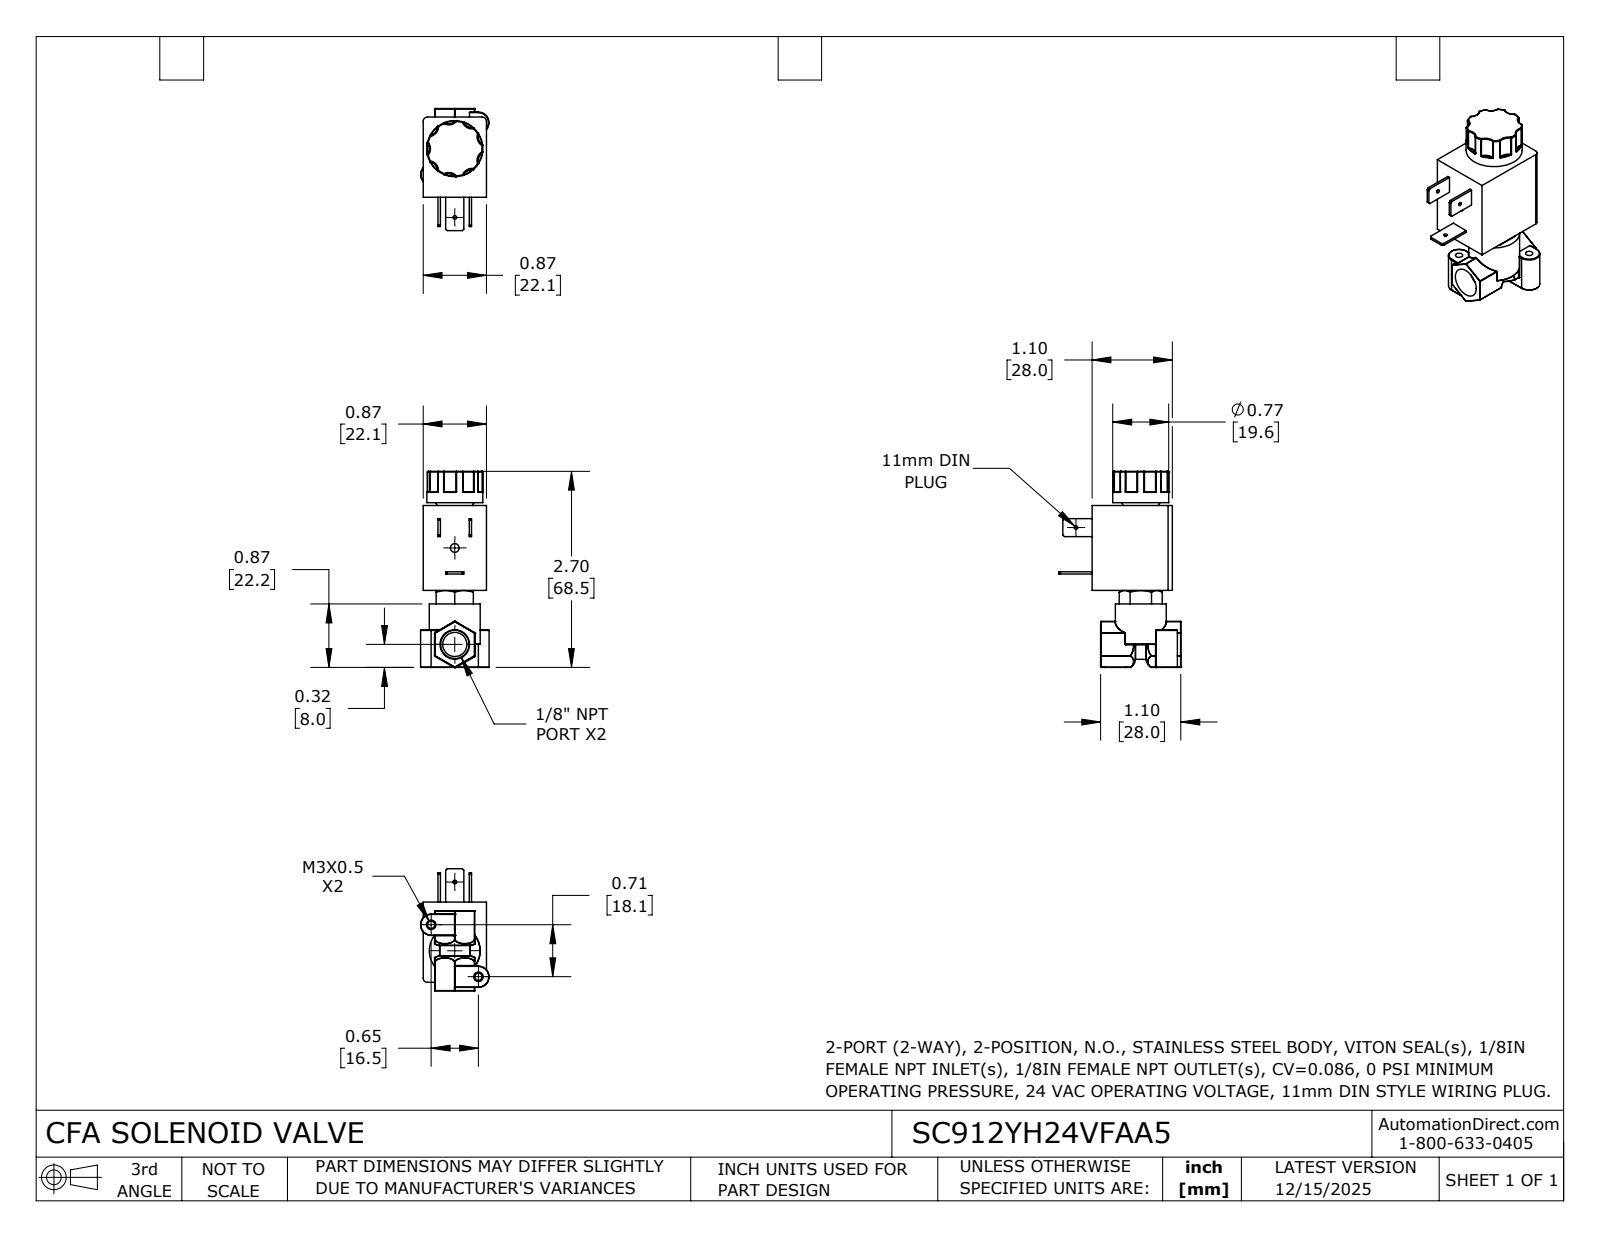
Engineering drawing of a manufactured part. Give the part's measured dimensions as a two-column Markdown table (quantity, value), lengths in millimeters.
| quantity | value |
| --- | --- |
| part name | SC912YH24VFAA5 |
| STEP written by | SolidWorks 2024 (CONFIG_CONTROL_DESIGN) |
| units | millimeters |
| bodies | 1 solid, 397 faces (76 planar, 110 cylindrical, 211 other) |
| overall size | 68.5 × 42.6 × 23.9 |
| volume | 28 500 mm³ |
| surface area | 9 064 mm² |
| round holes (diameter × count) | 1.3 × 2, 2.5 × 2, 3 × 1, 8.4 × 1 |
| round bosses / shafts (diameter × count) | 19.6 × 1, 17.8 × 1 |
| partial cylindrical surfaces (radius × count) | 0.1 × 29, 0.3 × 18, 0.2 × 12, 3.4 × 7, 0.4 × 2, 1.5 × 2, 3.4 × 2, 3.7 × 2 |
| main face-to-face distances | 22.1, 28, 29.6, 41.6, 11.9, 13.9, 0.8, 4.1, 18, 30.7 |
| hole center spacings | 17.1, 24.5, 33.7, 34.1 |
